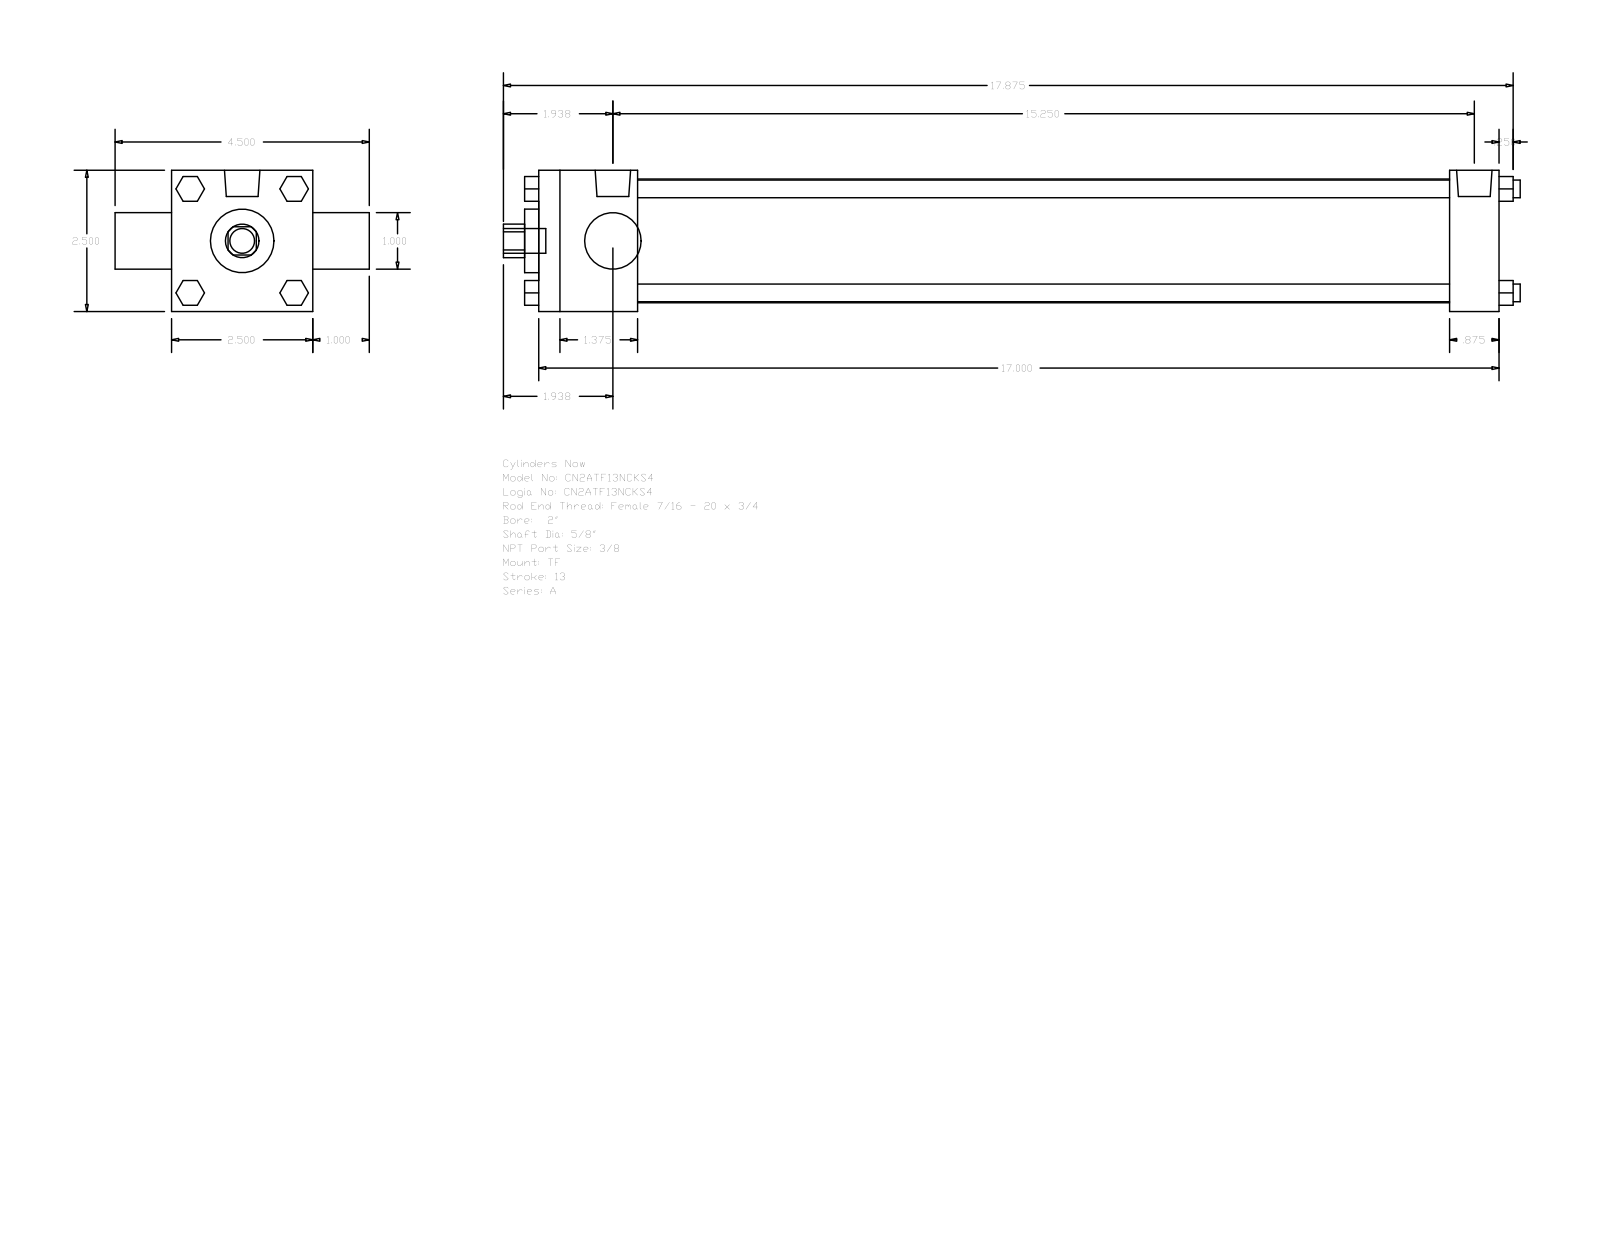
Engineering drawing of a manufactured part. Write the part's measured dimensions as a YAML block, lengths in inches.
part_name: "A_TF__0200_0.625"
step_written_by: "GSSL Pune (CONFIG_CONTROL_DESIGN)"
units: inches
bodies: {solids: 0, faces: 120, planar: 92, cylindrical: 28, other: 0}
overall_size: [18, 4.5, 2.5]
round_holes:
  - {diameter: 0.625, count: 1}
  - {diameter: 1, count: 1}
  - {diameter: 1.125, count: 1}
  - {diameter: 2.19, count: 1}
round_bosses_or_shafts:
  - {diameter: 0.313, count: 4}
  - {diameter: 0.219, count: 3}
  - {diameter: 0.627, count: 2}
  - {diameter: 0.437, count: 1}
partial_cylinders:
  - {radius: 0.297, count: 1}
face_to_face_distances: [2.5, 17, 1.75, 16.125, 14.375, 15.25, 0.875, 1, 3.5, 2]
